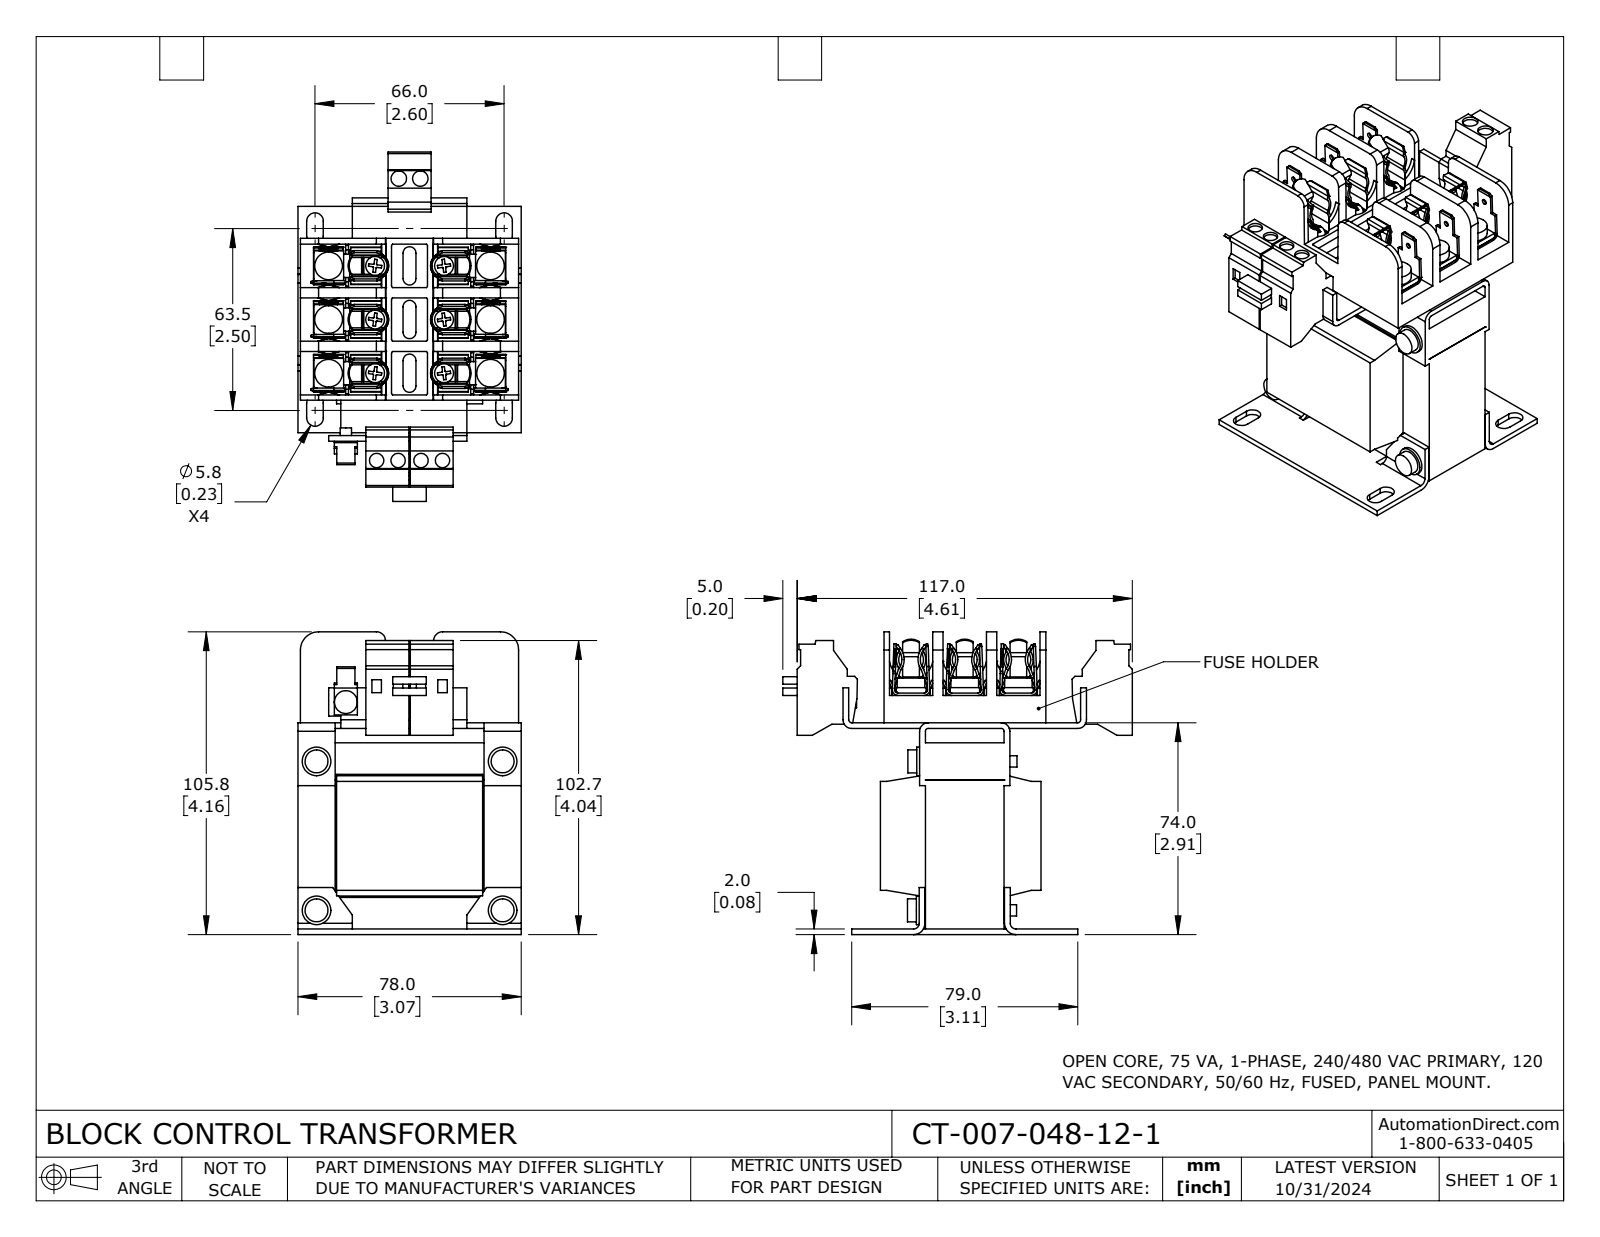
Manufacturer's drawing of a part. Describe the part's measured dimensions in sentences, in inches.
The part is named "CT-007-048-12-1". Its 3-D file was written by "SolidWorks 2023 (CONFIG_CONTROL_DESIGN)". It is 2 solids with 1636 faces: 1086 planar, 520 cylindrical and 30 other. Overall it measures 4.803 by 4.163 by 3.071 inches. Its volume is 18.86 cubic inches and its surface area 158 square inches. Round holes: 12 of diameter 0.074, 5 of diameter 0.205, 4 of diameter 0.197, 2 of diameter 0.213, 1 of diameter 0.205. Round bosses or shafts: 6 of diameter 0.38, 6 of diameter 0.19, 5 of diameter 0.315, 5 of diameter 0.157, 4 of diameter 0.394, 2 of diameter 0.177. Partial cylindrical surfaces (rounded edges, fillets, slot ends): 24 of radius 0.01, 20 of radius 0.05, 18 of radius 0.03, 14 of radius 0.072, 12 of radius 0.038, 12 of radius 0.04, 12 of radius 0.164, 9 of radius 0.097. The main face-to-face distances are 0.079, 2.835, 0.531, 0.512, 2.047, 0.738, 0.709, 0.02, 2.559, 2.913. The hole center spacings are 2.232, 2.354, 0.026, 0.026, 0.052, 0.738, 2.345, 3.886.
